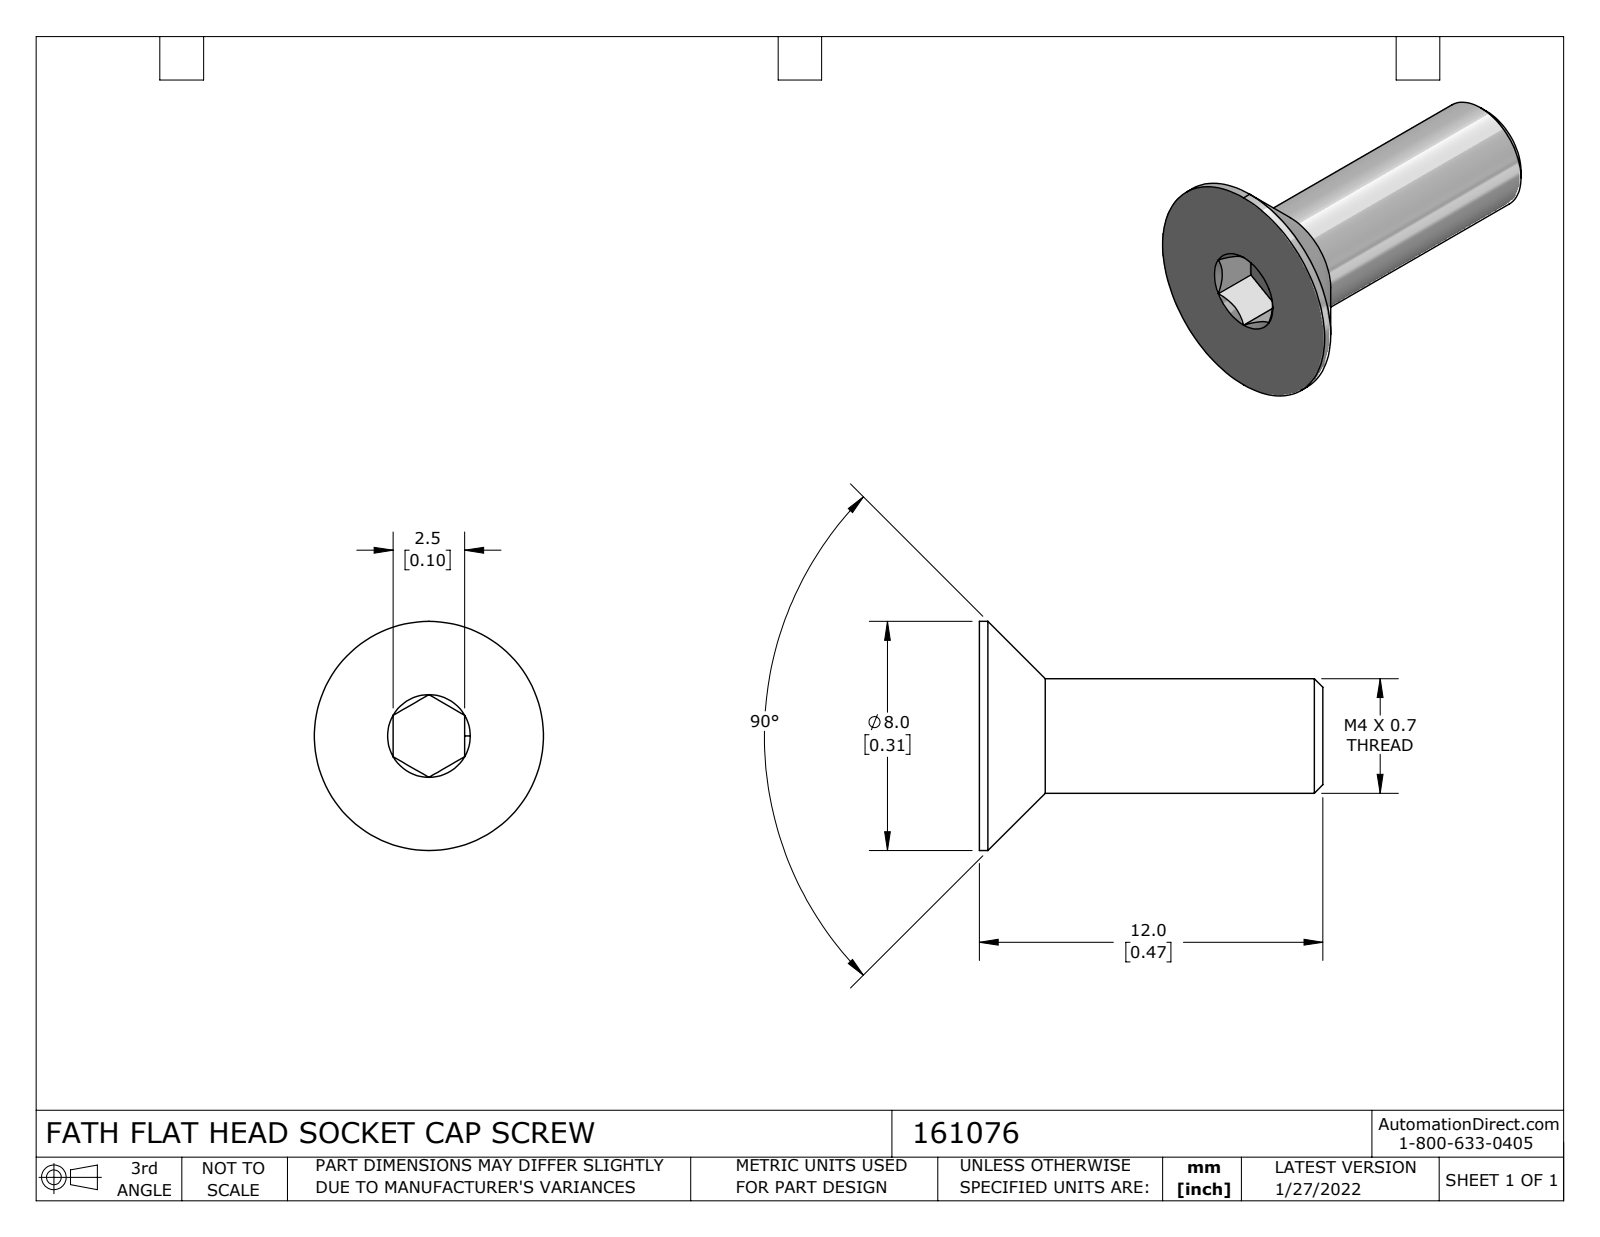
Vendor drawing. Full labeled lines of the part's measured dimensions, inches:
Part name (STEP PRODUCT): 161076
STEP written by: SolidWorks 2021 (CONFIG_CONTROL_DESIGN)
Units: inches
Bodies: 1 solid, 24 faces (9 planar, 4 cylindrical, 11 other)
Overall size (bounding box): 0.472 × 0.315 × 0.315
Volume: 0.011 in³ · Surface area: 0.398 in²
Round bosses / shafts (diameter × count): ⌀0.315 ×1, ⌀0.157 ×1
Main face-to-face distances: 0.472, 0.098, 0.409, 0.063
